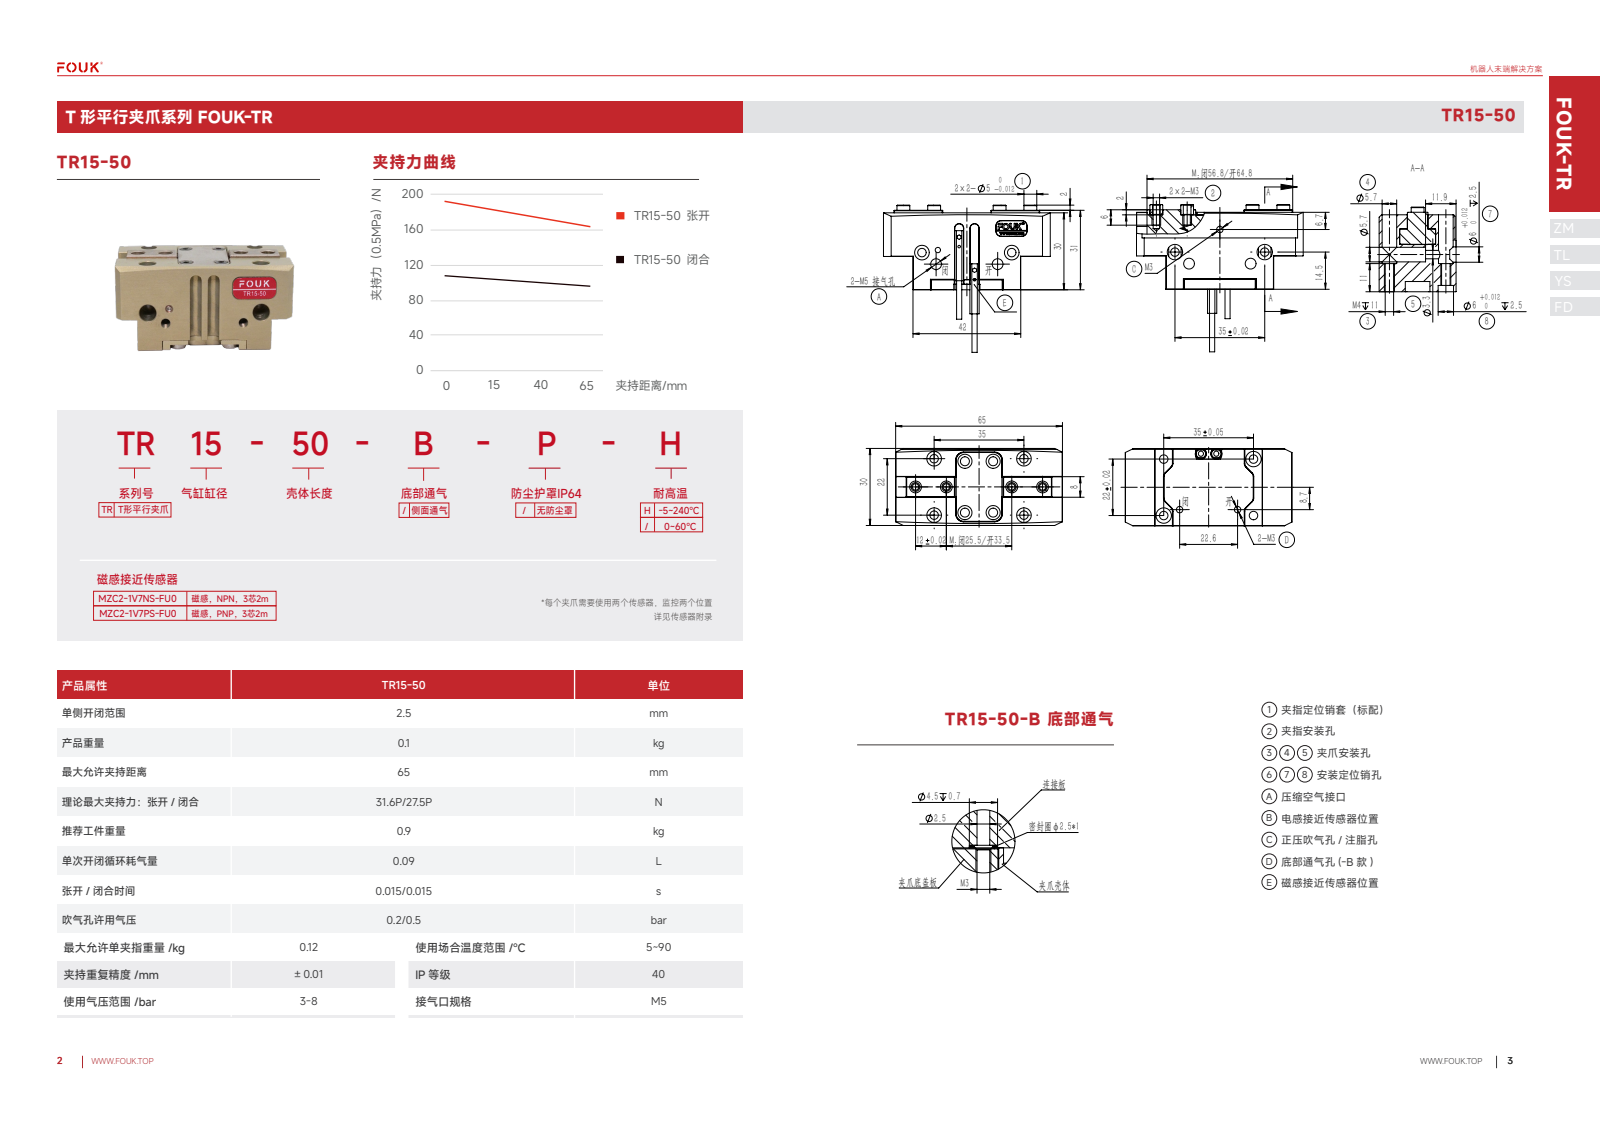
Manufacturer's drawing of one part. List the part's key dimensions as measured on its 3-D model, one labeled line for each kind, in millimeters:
Part name (STEP PRODUCT): 12x6-R2; TR15-50; 销套4×3×5
STEP written by: SolidWorks 2018 (CONFIG_CONTROL_DESIGN)
Units: millimetres
Bodies: 13 solids, 913 faces (476 planar, 240 cylindrical, 197 other)
Overall size (bounding box): 51.01 × 50 × 25.05
Volume: 24 862 mm³ · Surface area: 15 094 mm²
Round holes (diameter × count): ⌀2.5 ×7, ⌀2.6 ×7, ⌀4.8 ×6, ⌀2.05 ×4, ⌀3 ×4, ⌀4 ×4, ⌀5 ×4, ⌀1 ×2, ⌀1.6 ×2, ⌀1.8 ×2, ⌀0.8 ×1
Round bosses / shafts (diameter × count): ⌀4 ×2, ⌀2 ×2, ⌀1.6 ×1, ⌀0.7 ×1
Partial cylindrical surfaces — rounded edges, fillets, slot ends (radius × count): R0.12 ×30, R1.5 ×8, R2.1 ×6, R0.3 ×5, R1.4 ×4, R2 ×4, R2.4 ×4, R2.5 ×4
Main face-to-face distances: 7.5, 12.2, 3, 25, 15.2, 6, 24, 11, 8.8, 1.3
Hole centre spacings: 9.32, 9.33, 9.35, 10.57, 11.09, 15.44, 15.45, 17.22
